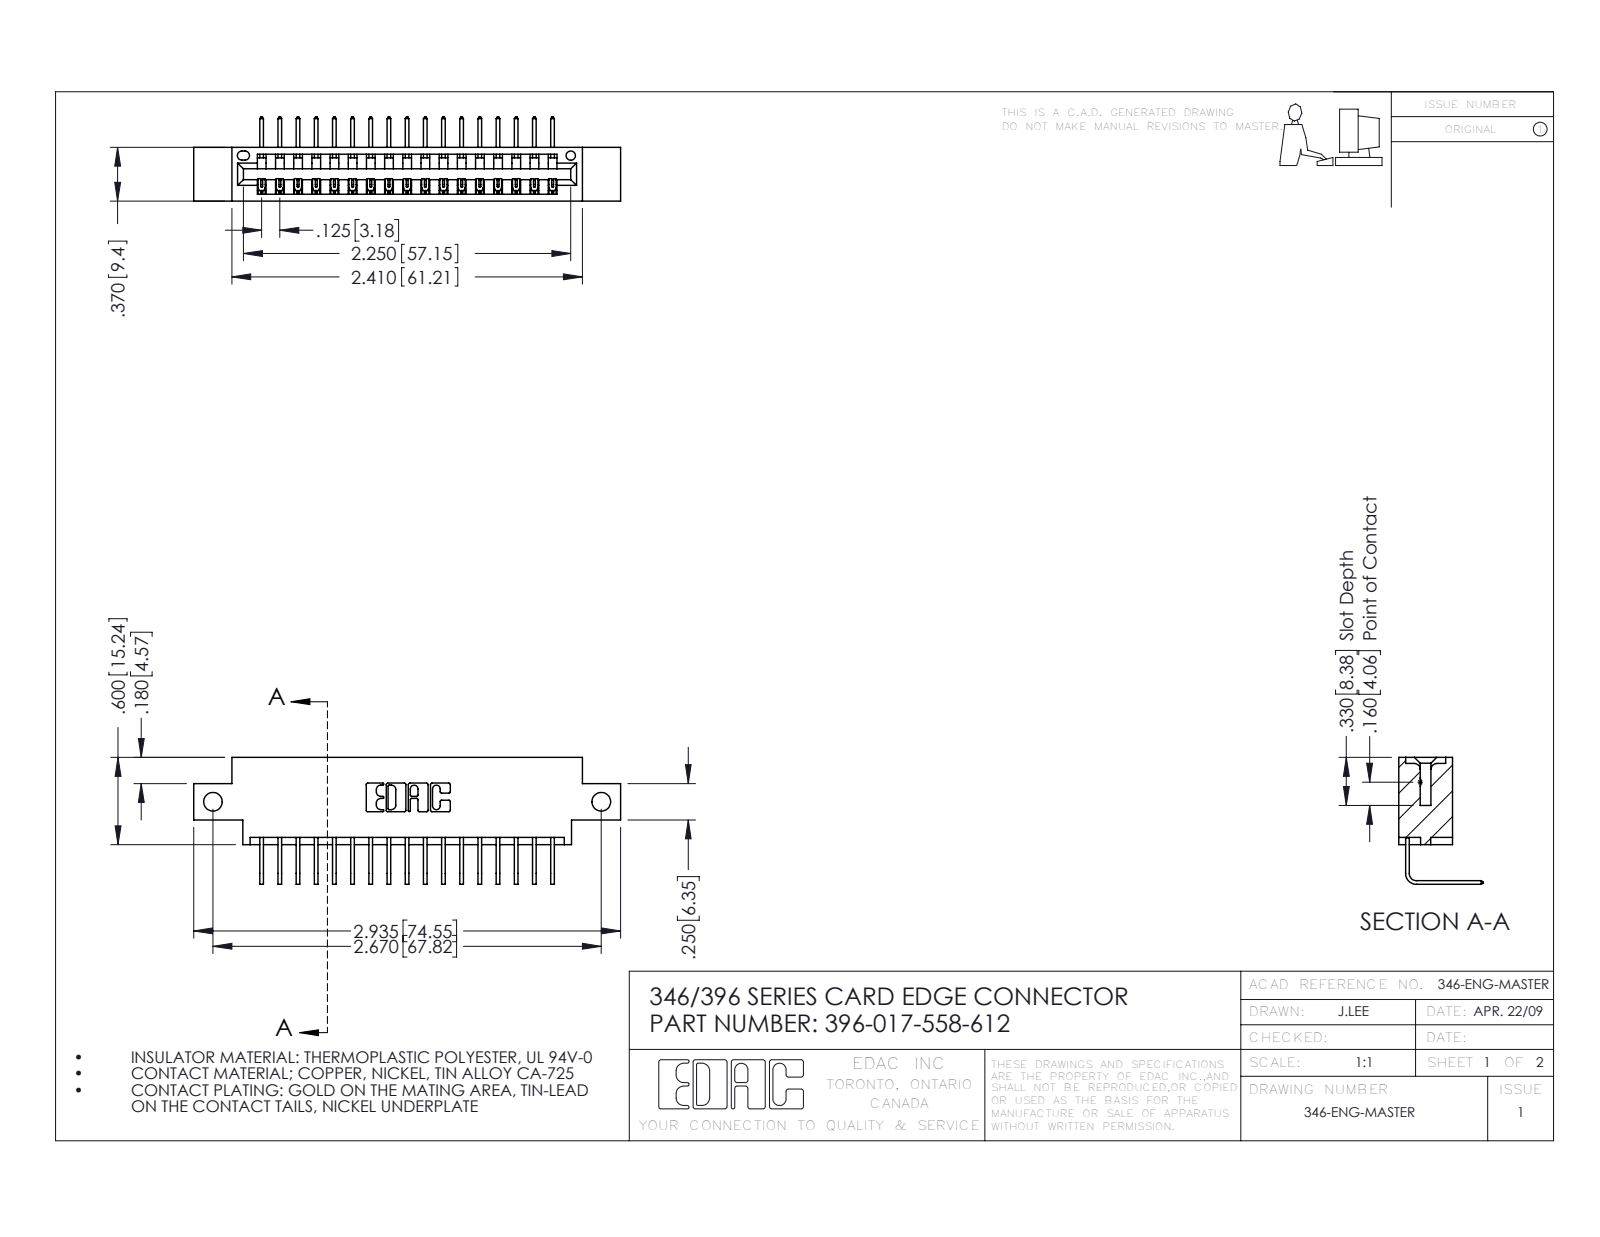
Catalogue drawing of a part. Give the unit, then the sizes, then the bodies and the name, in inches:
Units: inches
Overall size (bounding box): 2.935 × 0.873 × 0.58
Round holes (diameter × count): ⌀0.128 ×2, ⌀0.064 ×1
Partial cylindrical surfaces — rounded edges, fillets, slot ends (radius × count): R0.006 ×34, R0.01 ×22, R0.007 ×6, R0.031 ×6, R0.026 ×3, R0.031 ×2, R0.04 ×2, R0.014 ×1
Main face-to-face distances: 0.322, 0.37, 0.048, 0.25, 0.298, 0.025, 0.072, 0.148, 0.222, 0.1
Hole centre spacings: 2.67
Volume: 0.414 in³ · Surface area: 13.26 in²
Bodies: 18 solids, 1146 faces (794 planar, 352 cylindrical, 0 other)
Part name (STEP PRODUCT): 345-292-001_558 Tail - 2; 396-017-558-612; 346 Part_0.170 Offset - Side Mount
STEP written by: SolidWorks 2016 (CONFIG_CONTROL_DESIGN)
